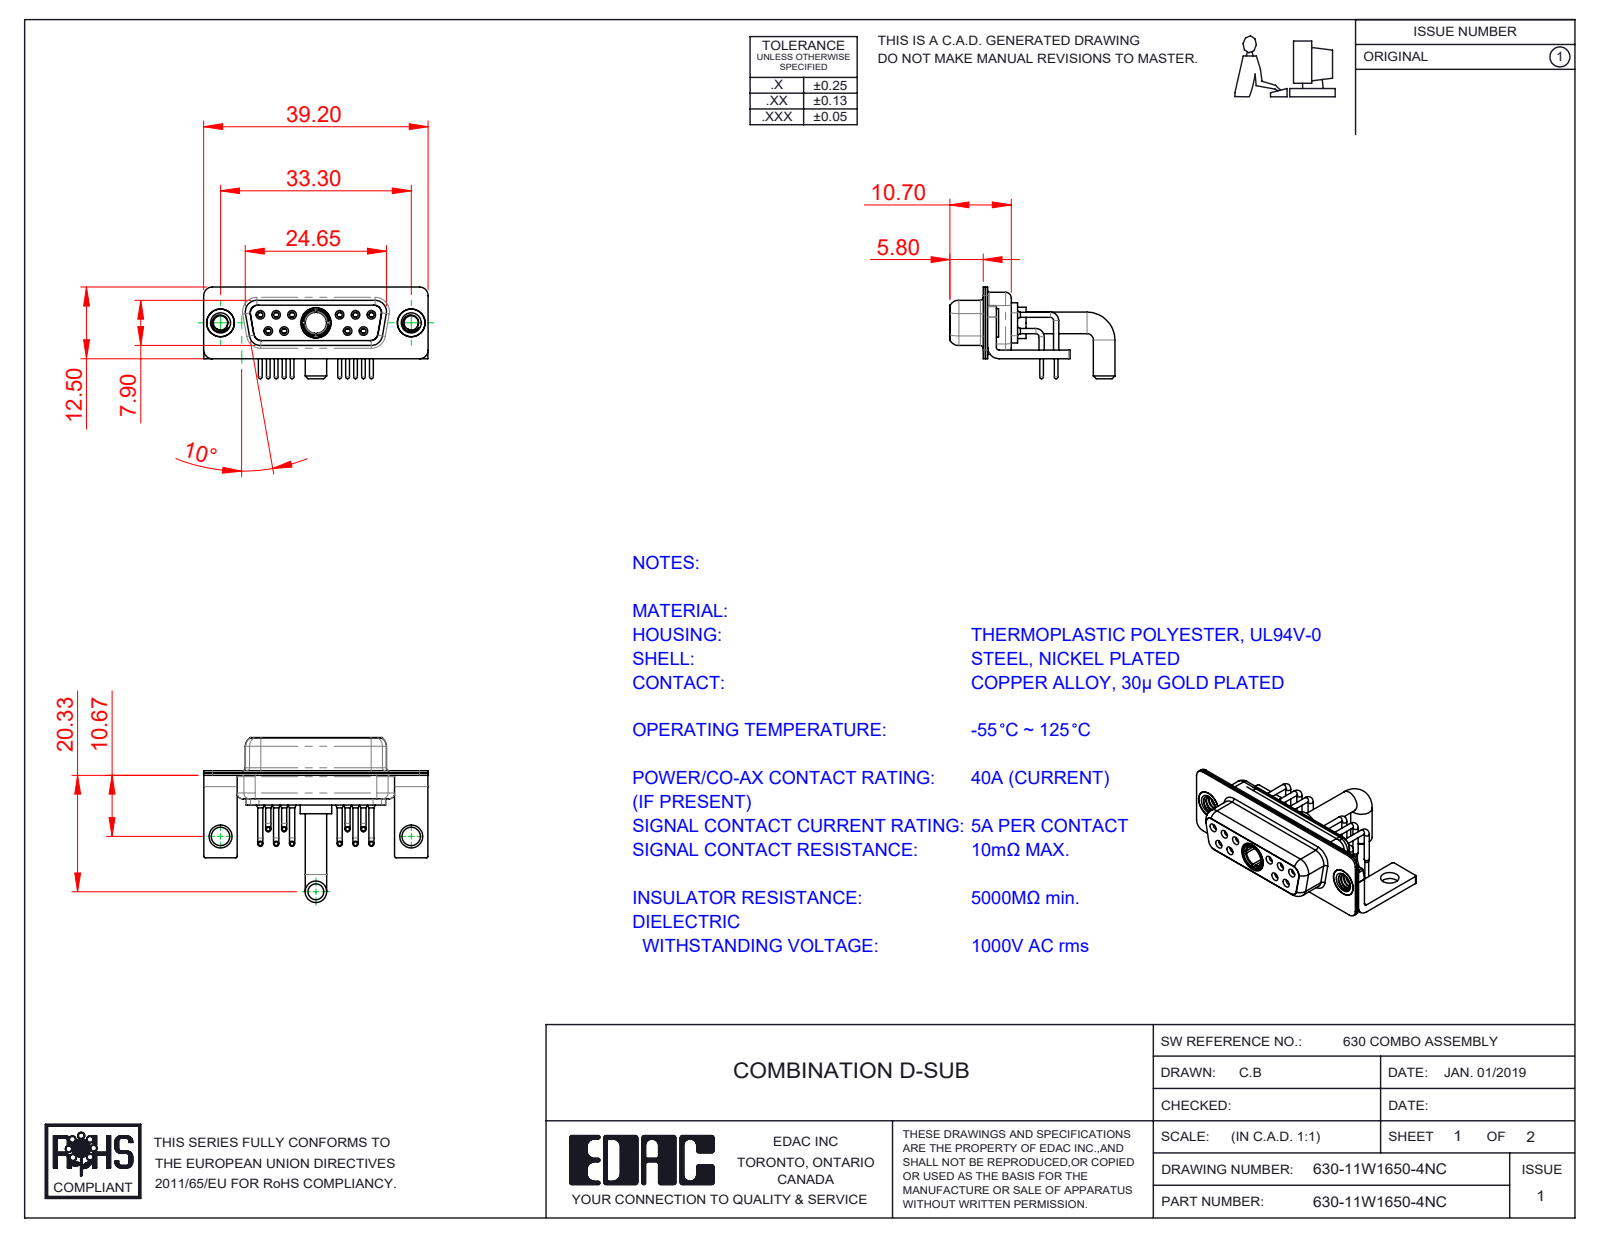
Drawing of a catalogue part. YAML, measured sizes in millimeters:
part_name: "630Combo Shell Front_15 Contacts; 630-11W1650-4NC; 630Combo Contact Row 2; 630Combo Contact Row 1 (+5 more)"
step_written_by: "SolidWorks 2020 (CONFIG_CONTROL_DESIGN)"
units: millimeters
bodies: {solids: 19, faces: 925, planar: 266, cylindrical: 410, other: 249}
overall_size: [39.2, 28.8, 16]
volume: 3059
surface_area: 6988
round_holes:
  - {diameter: 0.9, count: 10}
  - {diameter: 1.1, count: 10}
  - {diameter: 1.5, count: 10}
  - {diameter: 2, count: 10}
  - {diameter: 1.7, count: 6}
  - {diameter: 1.6, count: 4}
  - {diameter: 4.85, count: 3}
  - {diameter: 2.5, count: 2}
  - {diameter: 3.2, count: 2}
  - {diameter: 4, count: 2}
  - {diameter: 4.05, count: 2}
  - {diameter: 3.7, count: 1}
round_bosses_or_shafts:
  - {diameter: 0.9, count: 10}
  - {diameter: 0.65, count: 10}
  - {diameter: 1.6, count: 6}
  - {diameter: 5, count: 2}
  - {diameter: 4.95, count: 2}
  - {diameter: 4.8, count: 2}
  - {diameter: 3.75, count: 2}
  - {diameter: 5.5, count: 1}
partial_cylinders:
  - {radius: 0.25, count: 16}
  - {radius: 1.5, count: 16}
  - {radius: 2, count: 13}
  - {radius: 1.35, count: 12}
  - {radius: 1.6, count: 8}
  - {radius: 0.5, count: 5}
  - {radius: 0.6, count: 4}
  - {radius: 0.65, count: 4}
face_to_face_distances: [0.4, 0.8, 1.4, 0.45, 8.45, 1.5, 1.8, 8.9, 6.2, 2.3]
hole_center_spacings: [3.16, 2.77, 13.85, 11.08, 16.62, 5.03, 5.04, 5.54]
